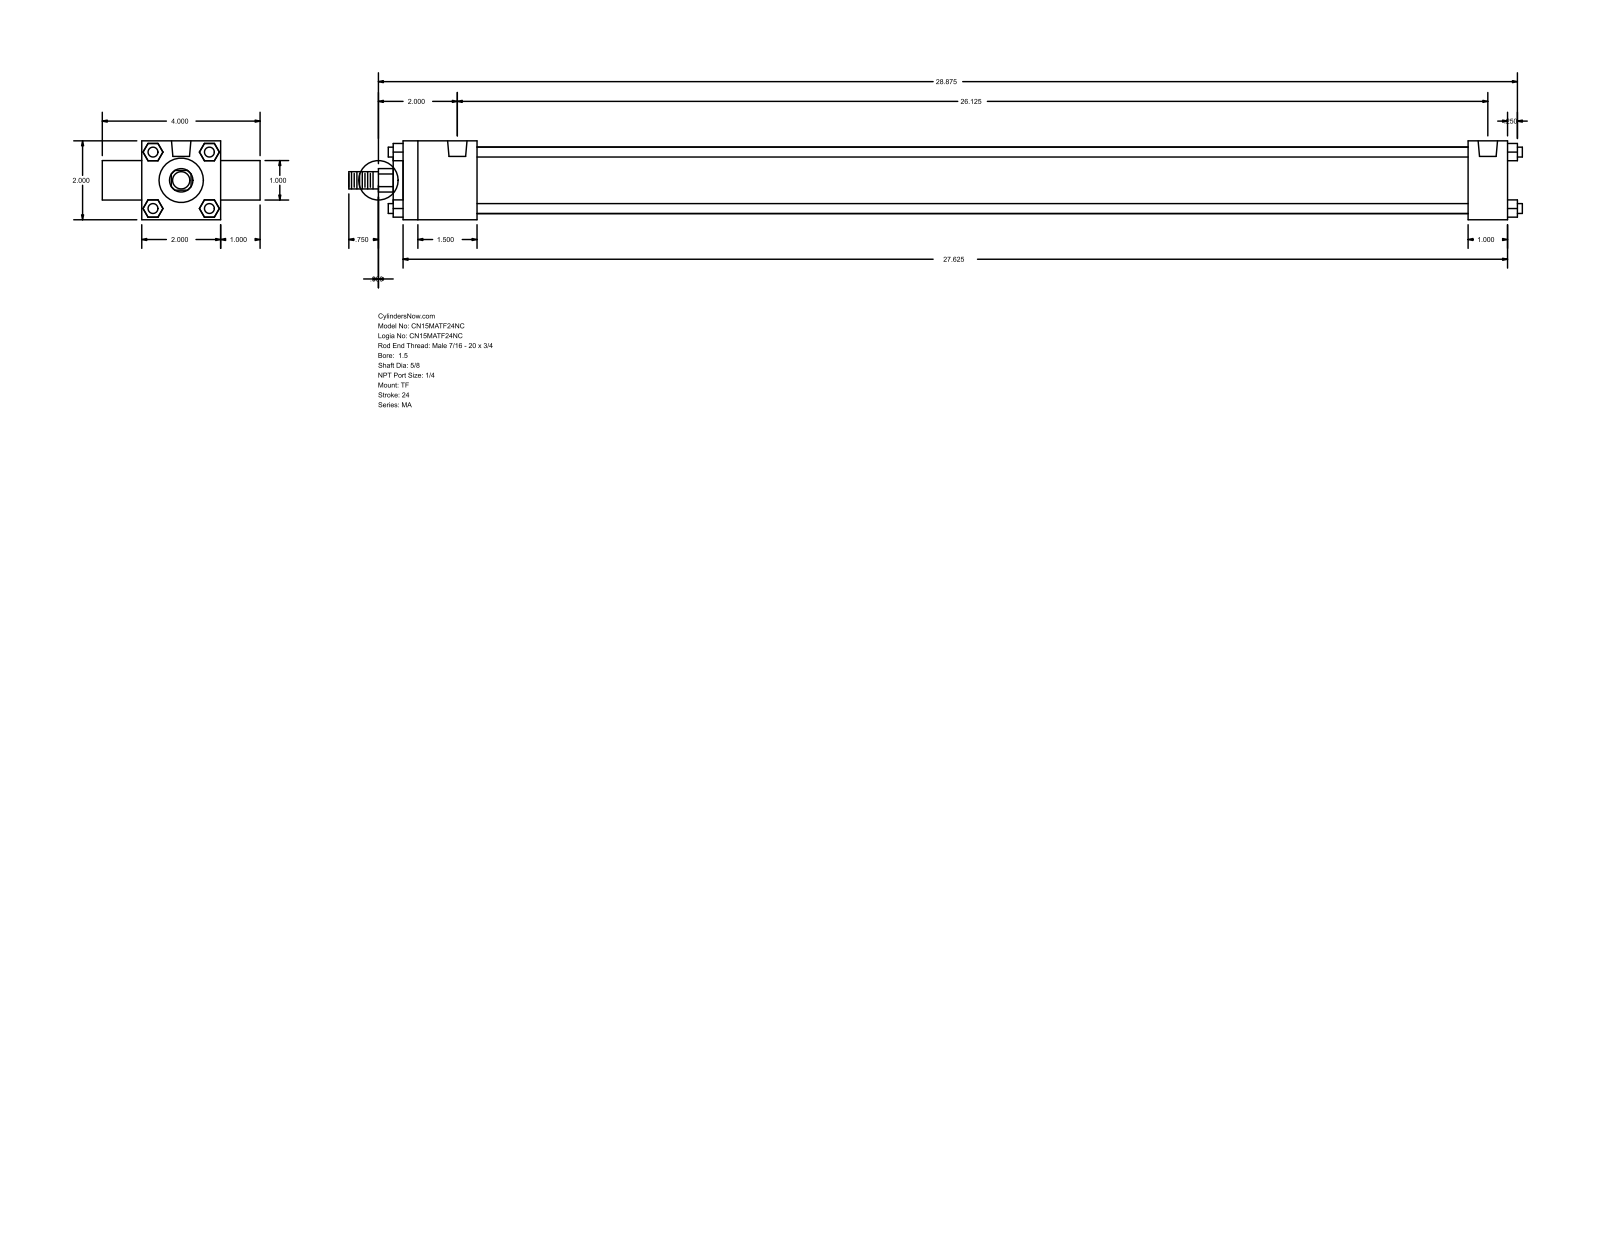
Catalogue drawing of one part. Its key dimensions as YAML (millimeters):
part_name: "MA_TF__0150_0.625"
step_written_by: "GSSL Pune (CONFIG_CONTROL_DESIGN)"
units: millimeters
bodies: {solids: 0, faces: 120, planar: 92, cylindrical: 28, other: 0}
overall_size: [755.65, 101.6, 50.8]
round_holes:
  - {diameter: 7.94, count: 3}
  - {diameter: 12.49, count: 2}
round_bosses_or_shafts:
  - {diameter: 6.35, count: 4}
  - {diameter: 42.93, count: 1}
  - {diameter: 28.57, count: 1}
  - {diameter: 25.4, count: 1}
  - {diameter: 15.88, count: 1}
  - {diameter: 11.11, count: 1}
partial_cylinders:
  - {radius: 7.54, count: 1}
face_to_face_distances: [50.8, 711.2, 25.4, 76.2, 47.62, 685.79, 638.17, 663.58, 25.41, 6.35]
hole_center_spacings: [663.58]
